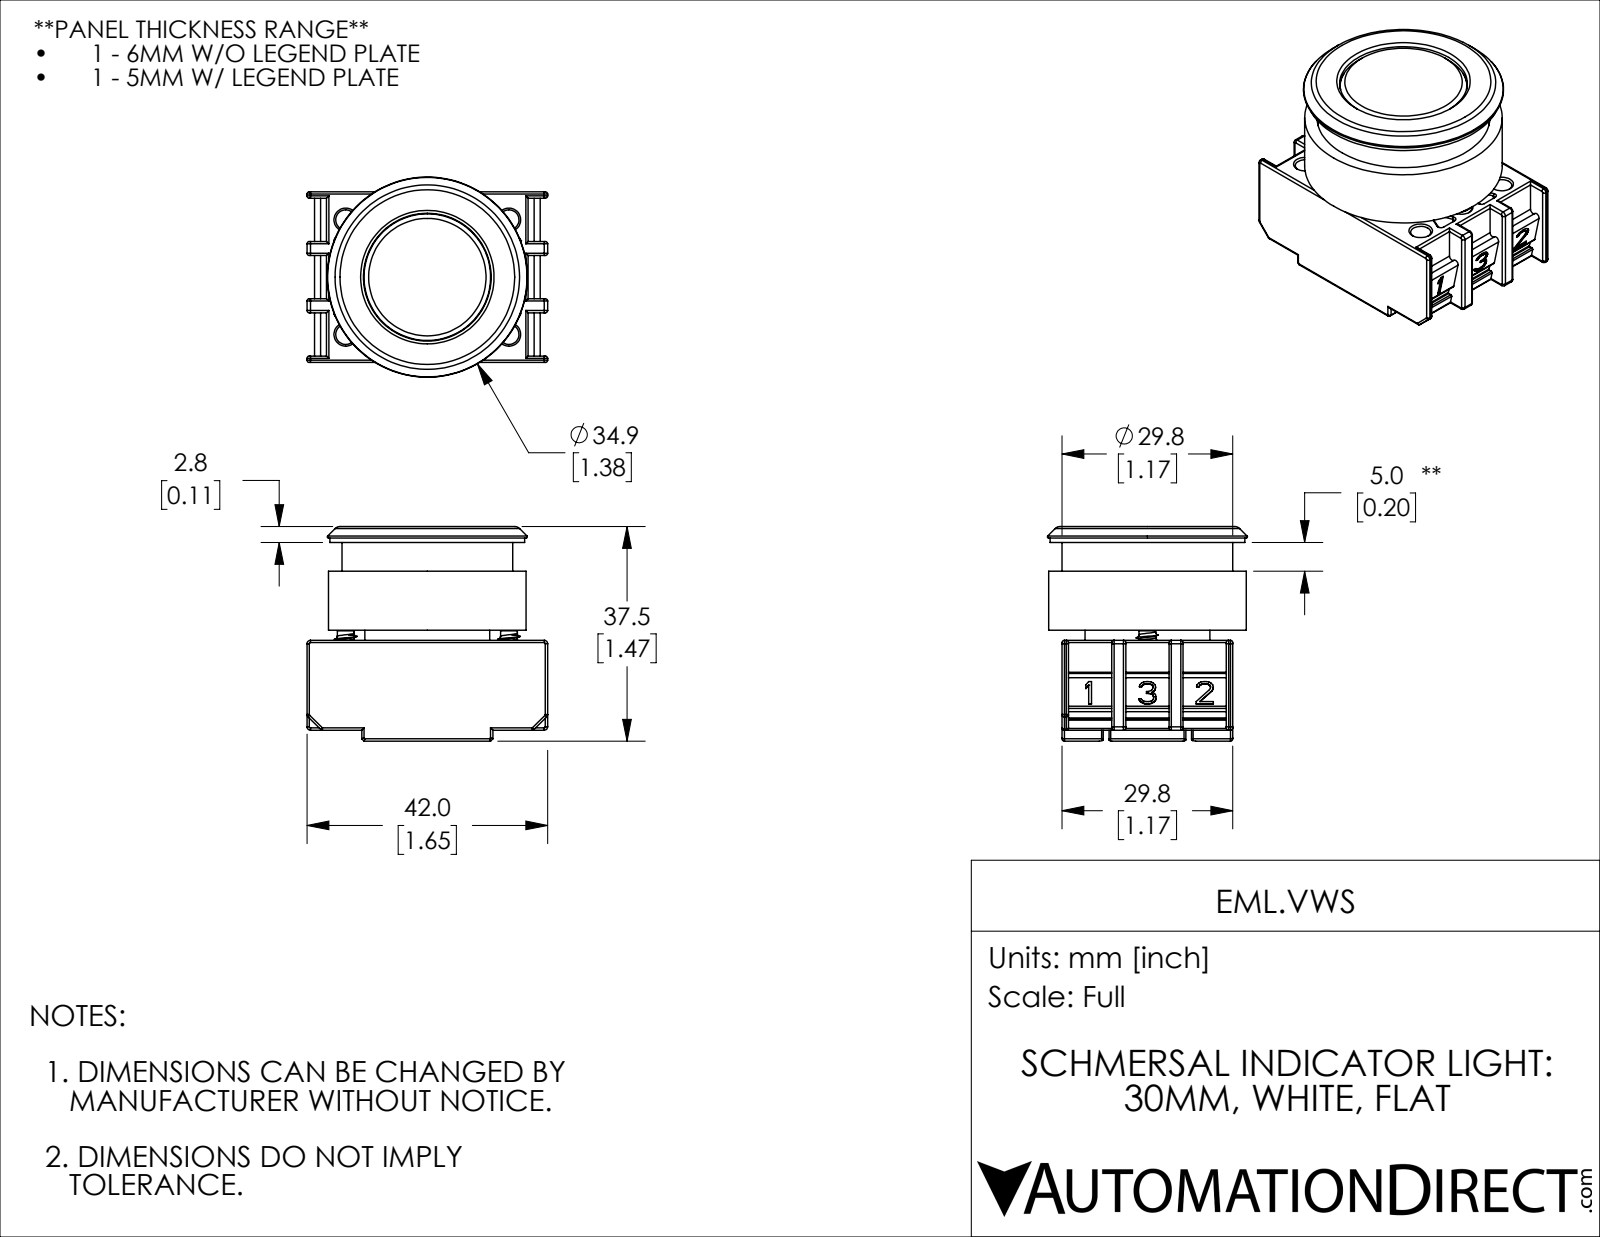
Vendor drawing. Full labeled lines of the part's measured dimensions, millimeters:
Part name (STEP PRODUCT): EML.VWS
STEP written by: SolidWorks 2019 (CONFIG_CONTROL_DESIGN)
Units: millimetres
Bodies: 3 solids, 1372 faces (495 planar, 474 cylindrical, 403 other)
Overall size (bounding box): 42 × 37.45 × 34.93
Volume: 22 251 mm³ · Surface area: 21 607 mm²
Round holes (diameter × count): ⌀3.5 ×6, ⌀5.15 ×6, ⌀11 ×1, ⌀12.6 ×1, ⌀15 ×1, ⌀18 ×1, ⌀22.3 ×1, ⌀24.2 ×1, ⌀26 ×1, ⌀27 ×1, ⌀30.2 ×1
Round bosses / shafts (diameter × count): ⌀4.8 ×2, ⌀2.93 ×2, ⌀34.5 ×1, ⌀34 ×1, ⌀29.8 ×1, ⌀25.5 ×1, ⌀24 ×1, ⌀23.8 ×1
Partial cylindrical surfaces — rounded edges, fillets, slot ends (radius × count): R0.4 ×115, R0.3 ×48, R0.2 ×28, R0.6 ×8, R0.5 ×6, R0.1 ×2, R0.6 ×2, R0.8 ×2
Main face-to-face distances: 29.8, 14.7, 1.75, 16.45, 3.4, 10, 1.9, 19.35, 19.65, 17.9
Hole centre spacings: 10, 17.41, 30.2, 28.5, 14.25, 20, 34.82
